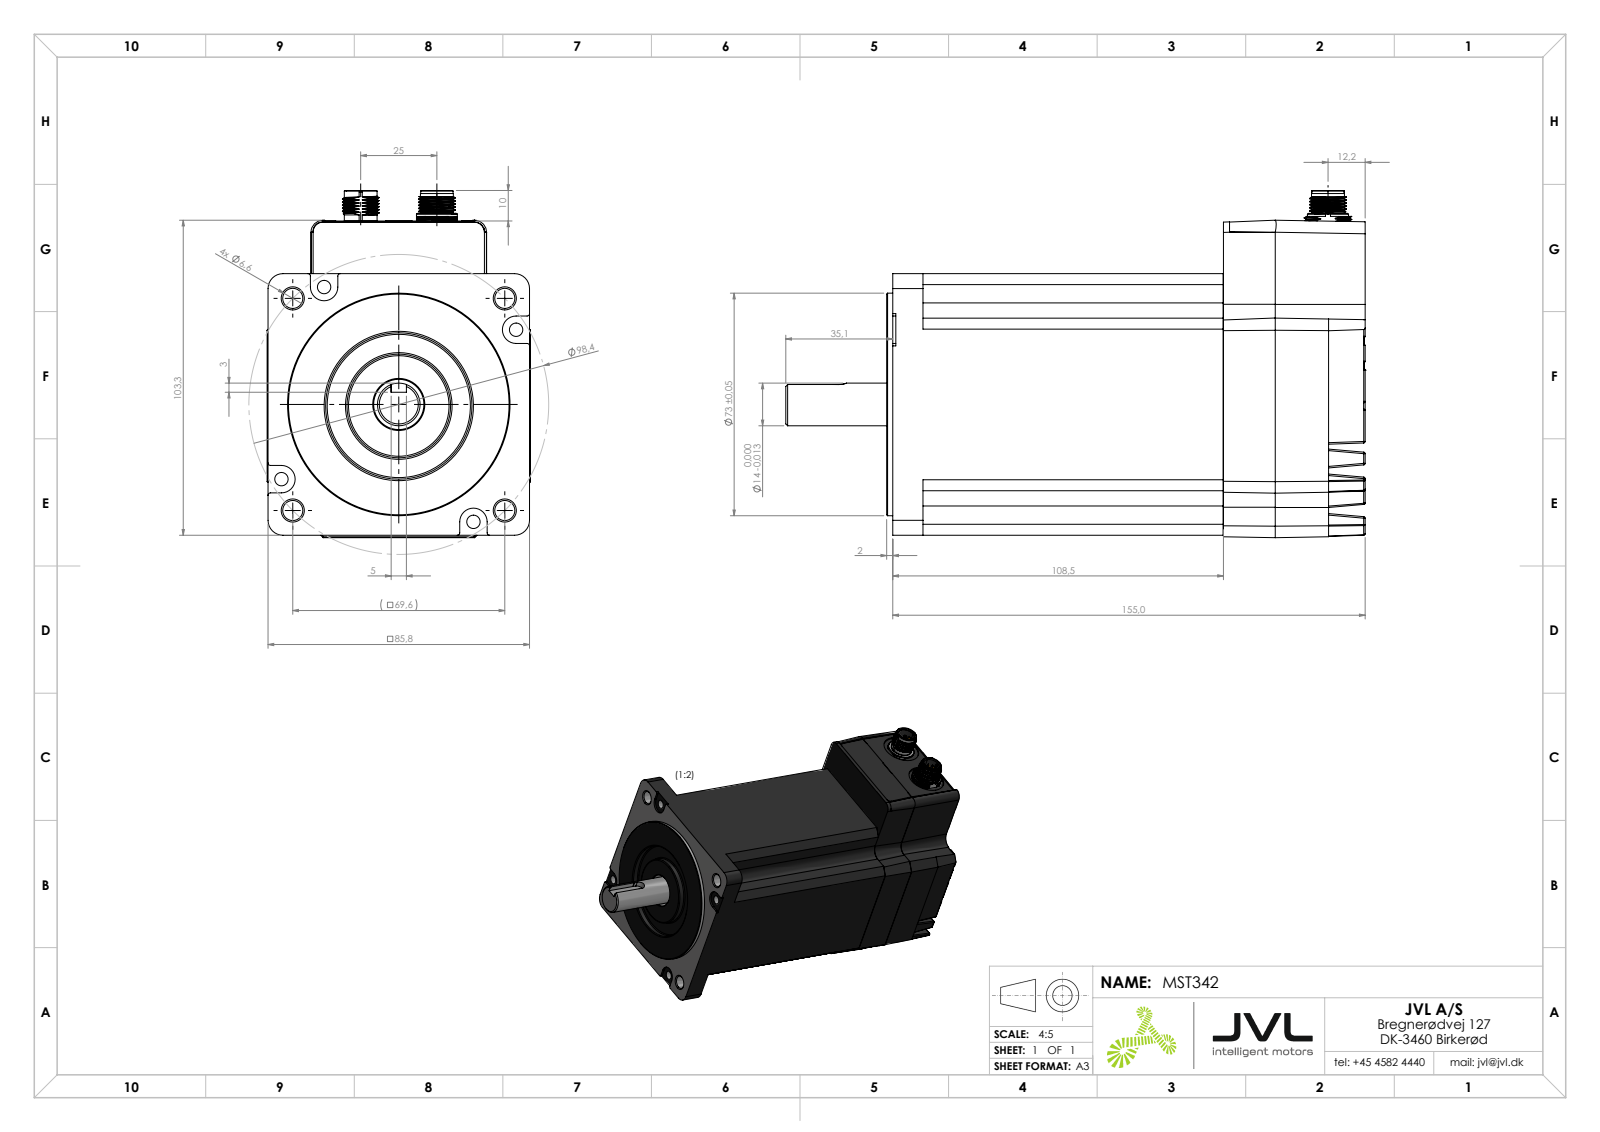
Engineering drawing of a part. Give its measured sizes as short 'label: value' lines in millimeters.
name: MST340C50BT2MP9.0J (back); MIS342 motor single shaft; MST342
written by: SolidWorks 2023 (AUTOMOTIVE_DESIGN)
unit: mm
bodies: 2 solids, 1349 faces (427 planar, 549 cylindrical, 373 other)
size: 190.1 × 113.87 × 86.41
volume: 1 039 000 mm³; area: 111 133 mm²
holes: 12× ⌀1, 8× ⌀1.1, 5× ⌀3, 4× ⌀4.3, 4× ⌀4.4, 4× ⌀6.6, 2× ⌀19, 1× ⌀1.7, 1× ⌀8.2, 1× ⌀8.85, 1× ⌀8.9, 1× ⌀16
bosses: 8× ⌀0.85, 8× ⌀0.8, 4× ⌀1.5, 1× ⌀73, 1× ⌀34, 1× ⌀14, 1× ⌀13.5, 1× ⌀12.1
rounds: 167× R0.5, 11× R0.1, 8× R0.8, 4× R0.2, 4× R0.4, 4× R4.5, 4× R4.9, 4× R5
face distances: 85.8, 14.6, 0.6, 71.2, 110.5, 2, 111.1, 109.1, 108.5, 45.9
hole spacings: 2.75, 2.74, 2.32, 8.4, 45.63, 64.54, 69.57, 4.21
